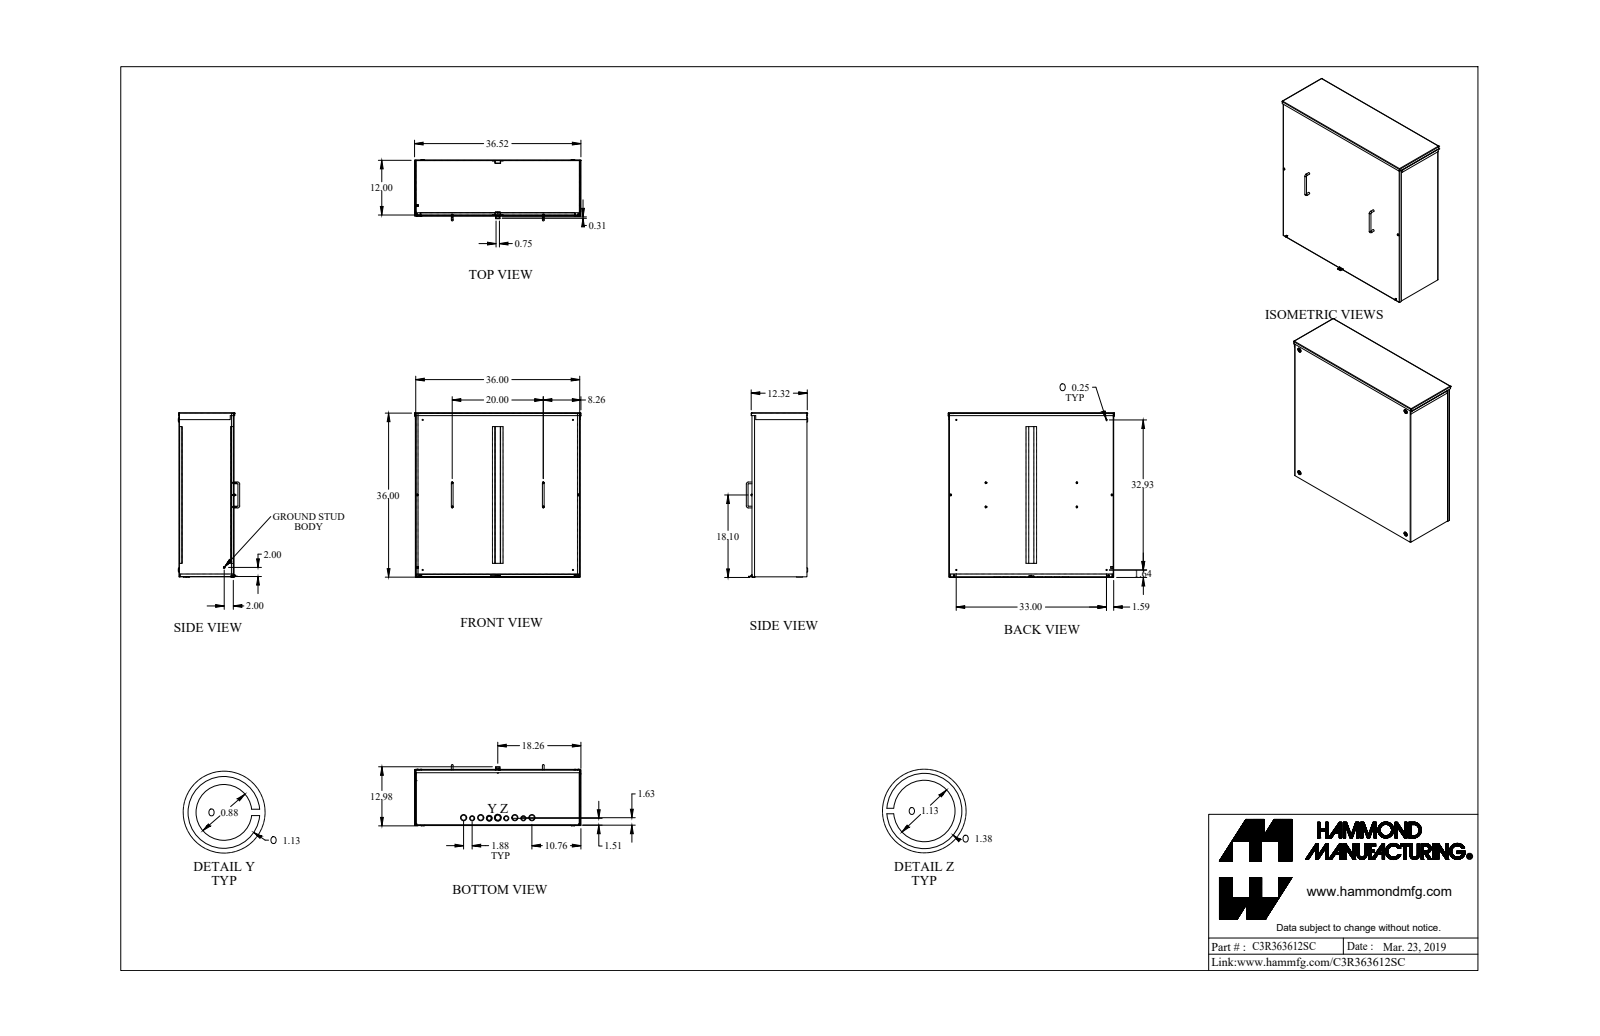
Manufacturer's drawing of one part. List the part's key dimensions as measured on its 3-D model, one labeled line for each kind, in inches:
Part name (STEP PRODUCT): C3R363612SC_Default
STEP written by: SolidWorks 2019 (CONFIG_CONTROL_DESIGN)
Units: inches
Bodies: 19 solids, 653 faces (342 planar, 193 cylindrical, 118 other)
Overall size (bounding box): 36.519 × 36.135 × 13.478
Volume: 343.3 in³ · Surface area: 9 558 in²
Round holes (diameter × count): ⌀0.156 ×5, ⌀0.17 ×4, ⌀0.203 ×4, ⌀0.25 ×4, ⌀1.125 ×3, ⌀0.875 ×2, ⌀0.875 ×2, ⌀1.125 ×2, ⌀0.125 ×1, ⌀0.137 ×1
Round bosses / shafts (diameter × count): ⌀0.375 ×9, ⌀0.19 ×8, ⌀1.125 ×4, ⌀0.367 ×4, ⌀1.375 ×3, ⌀1.375 ×2, ⌀0.375 ×2, ⌀0.125 ×1
Partial cylindrical surfaces — rounded edges, fillets, slot ends (radius × count): R0.036 ×28, R0.108 ×28, R0.109 ×8, R0.125 ×8, R0.156 ×2, R0.029 ×1, R0.086 ×1
Main face-to-face distances: 0.072, 12, 11.928, 12.072, 35.928, 36, 0.072, 35.856, 35.856, 35.928
Hole centre spacings: 20, 3.75, 7.5, 0.024, 1.879, 1.88, 5.3, 8.139
